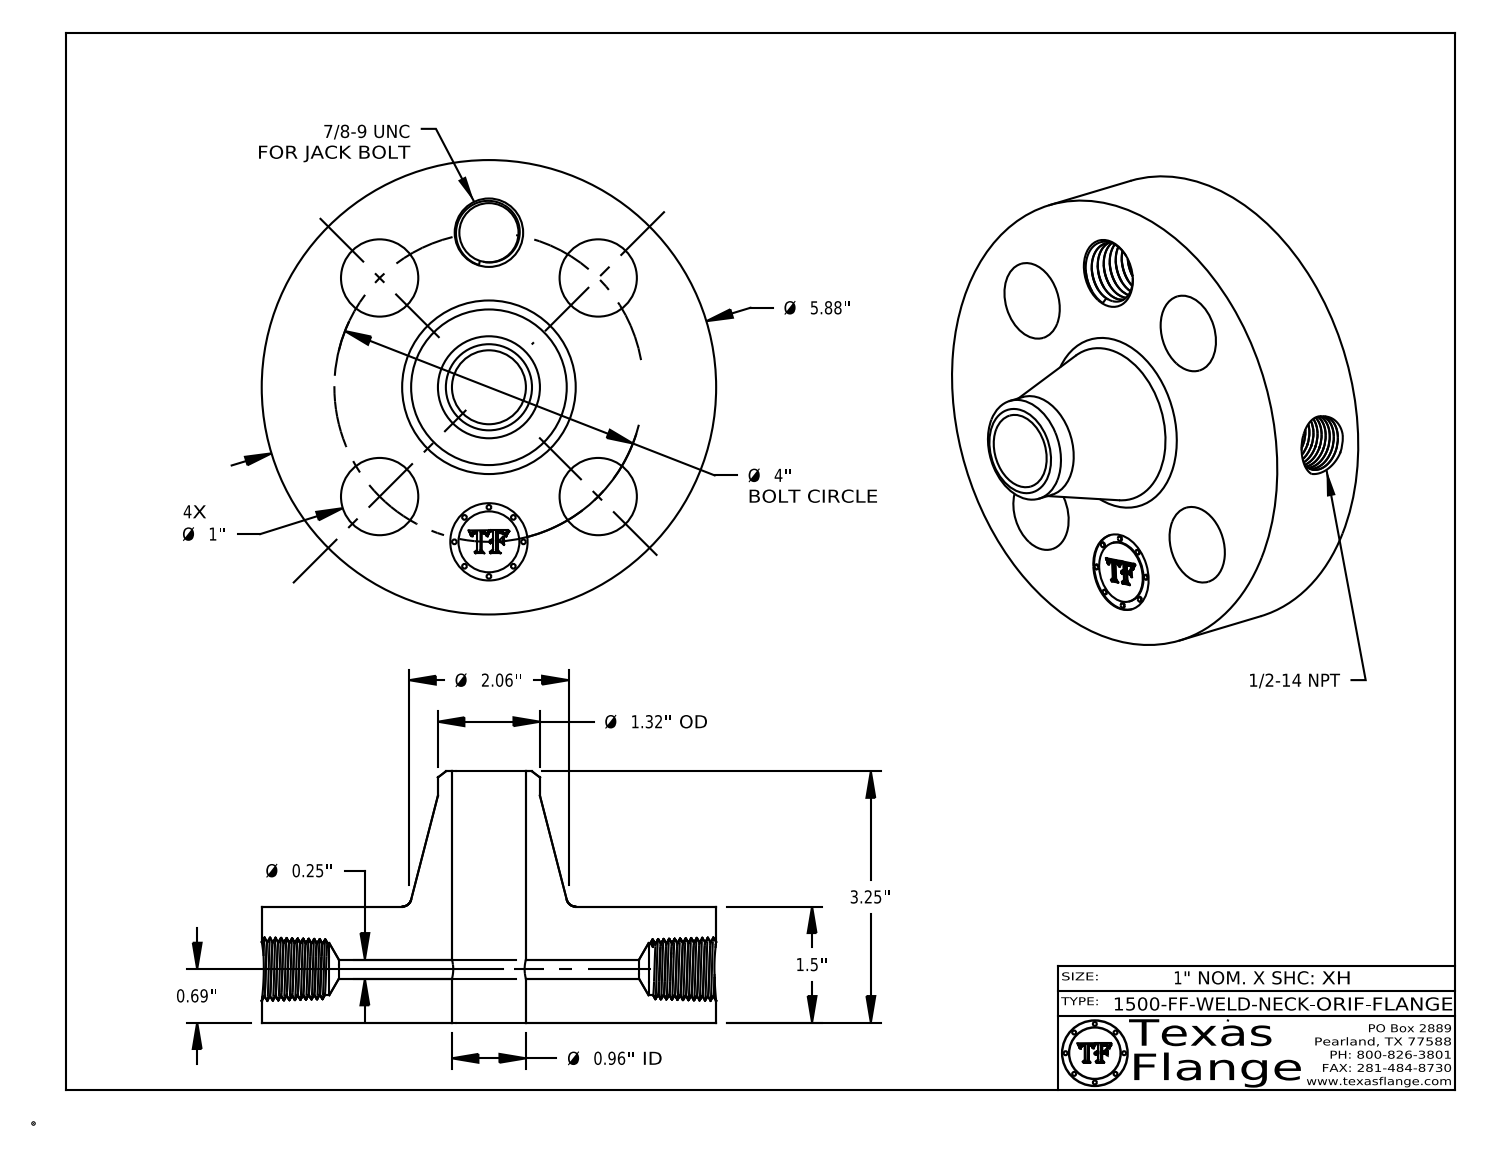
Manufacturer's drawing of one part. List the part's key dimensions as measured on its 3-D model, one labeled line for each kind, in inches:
Part name (STEP PRODUCT): 1500-FF-WELD-NECK
STEP written by: CATIA V5 STEP AP214 (AUTOMOTIVE_DESIGN)
Units: inches
Bodies: 1 solid, 746 faces (368 planar, 80 cylindrical, 298 other)
Overall size (bounding box): 5.88 × 5.88 × 3.25
Volume: 35.65 in³ · Surface area: 123.3 in²
Round holes (diameter × count): ⌀1 ×5, ⌀0.25 ×1, ⌀0.672 ×1, ⌀0.766 ×1, ⌀0.957 ×1
Round bosses / shafts (diameter × count): ⌀0.061 ×8, ⌀5.88 ×1, ⌀1.32 ×1, ⌀0.788 ×1
Main face-to-face distances: 1.5, 1.485, 0.015, 3.25, 1.765, 1.75, 0.298, 0.293, 0.054, 0.248
Hole centre spacings: 2, 1.531, 2.828, 3.695, 4
